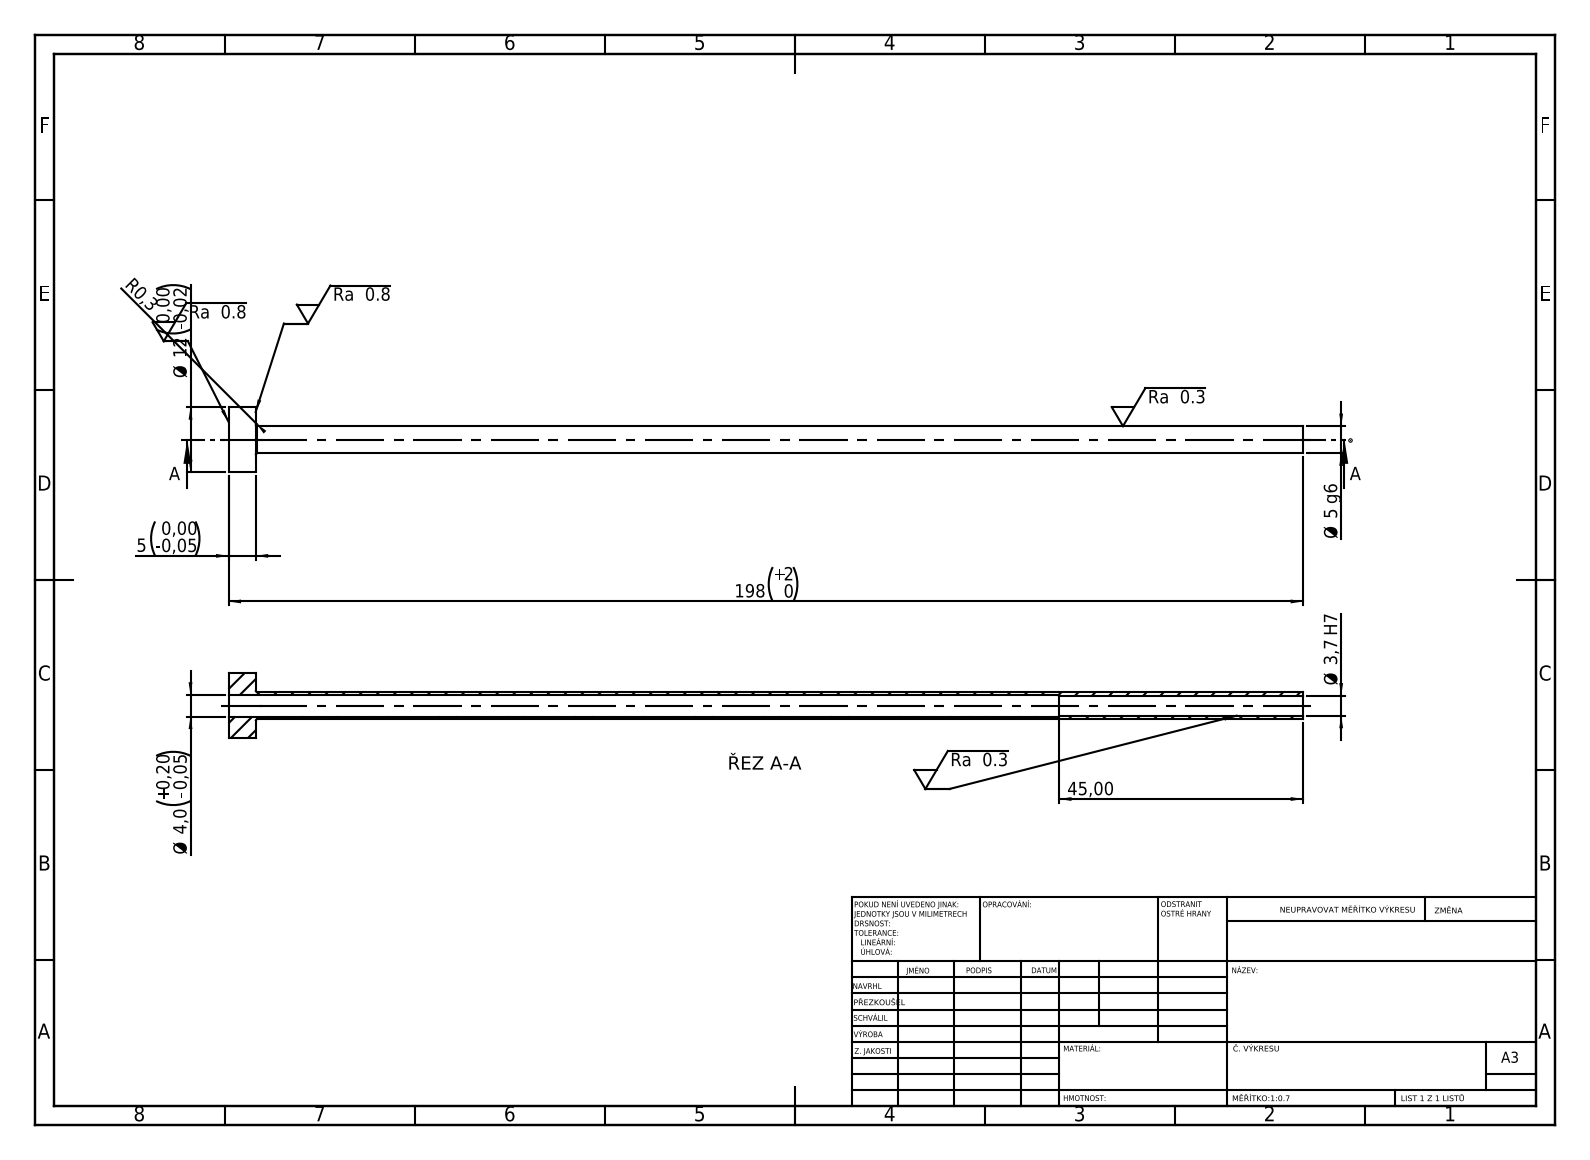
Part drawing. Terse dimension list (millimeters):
written by: SolidWorks 2019 (CONFIG_CONTROL_DESIGN)
unit: mm
bodies: 1 solid, 14 faces (4 planar, 8 cylindrical, 2 other)
size: 198 × 12 × 12
volume: 1 949 mm³; area: 5 869 mm²
holes: 1× ⌀3.7, 1× ⌀4
bosses: 1× ⌀12, 1× ⌀5
face distances: 5, 198, 193, 153, 148, 45
